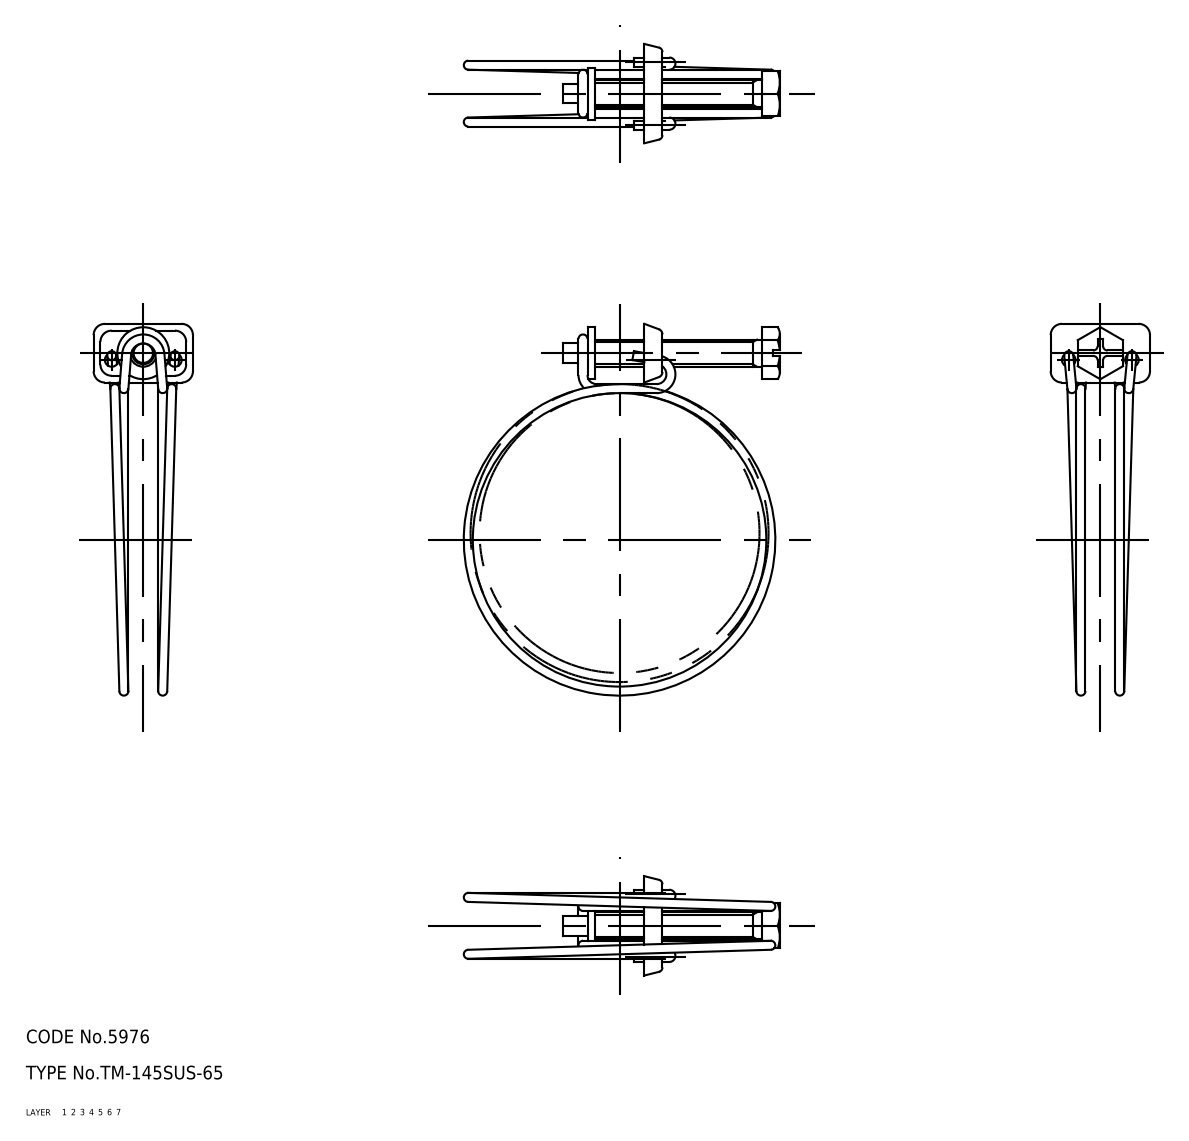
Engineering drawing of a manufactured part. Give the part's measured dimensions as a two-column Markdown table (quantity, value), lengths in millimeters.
| quantity | value |
| --- | --- |
| part name | screw; holder; band; TM_145SUS_65_22572_36 |
| STEP written by | CADfix (AUTOMOTIVE_DESIGN) |
| units | millimeters |
| bodies | 3 solids, 119 faces (0 planar, 0 cylindrical, 119 other) |
| overall size | 82.35 × 70 × 22 |
| volume | 3 700 mm³ |
| surface area | 5 334 mm² |
